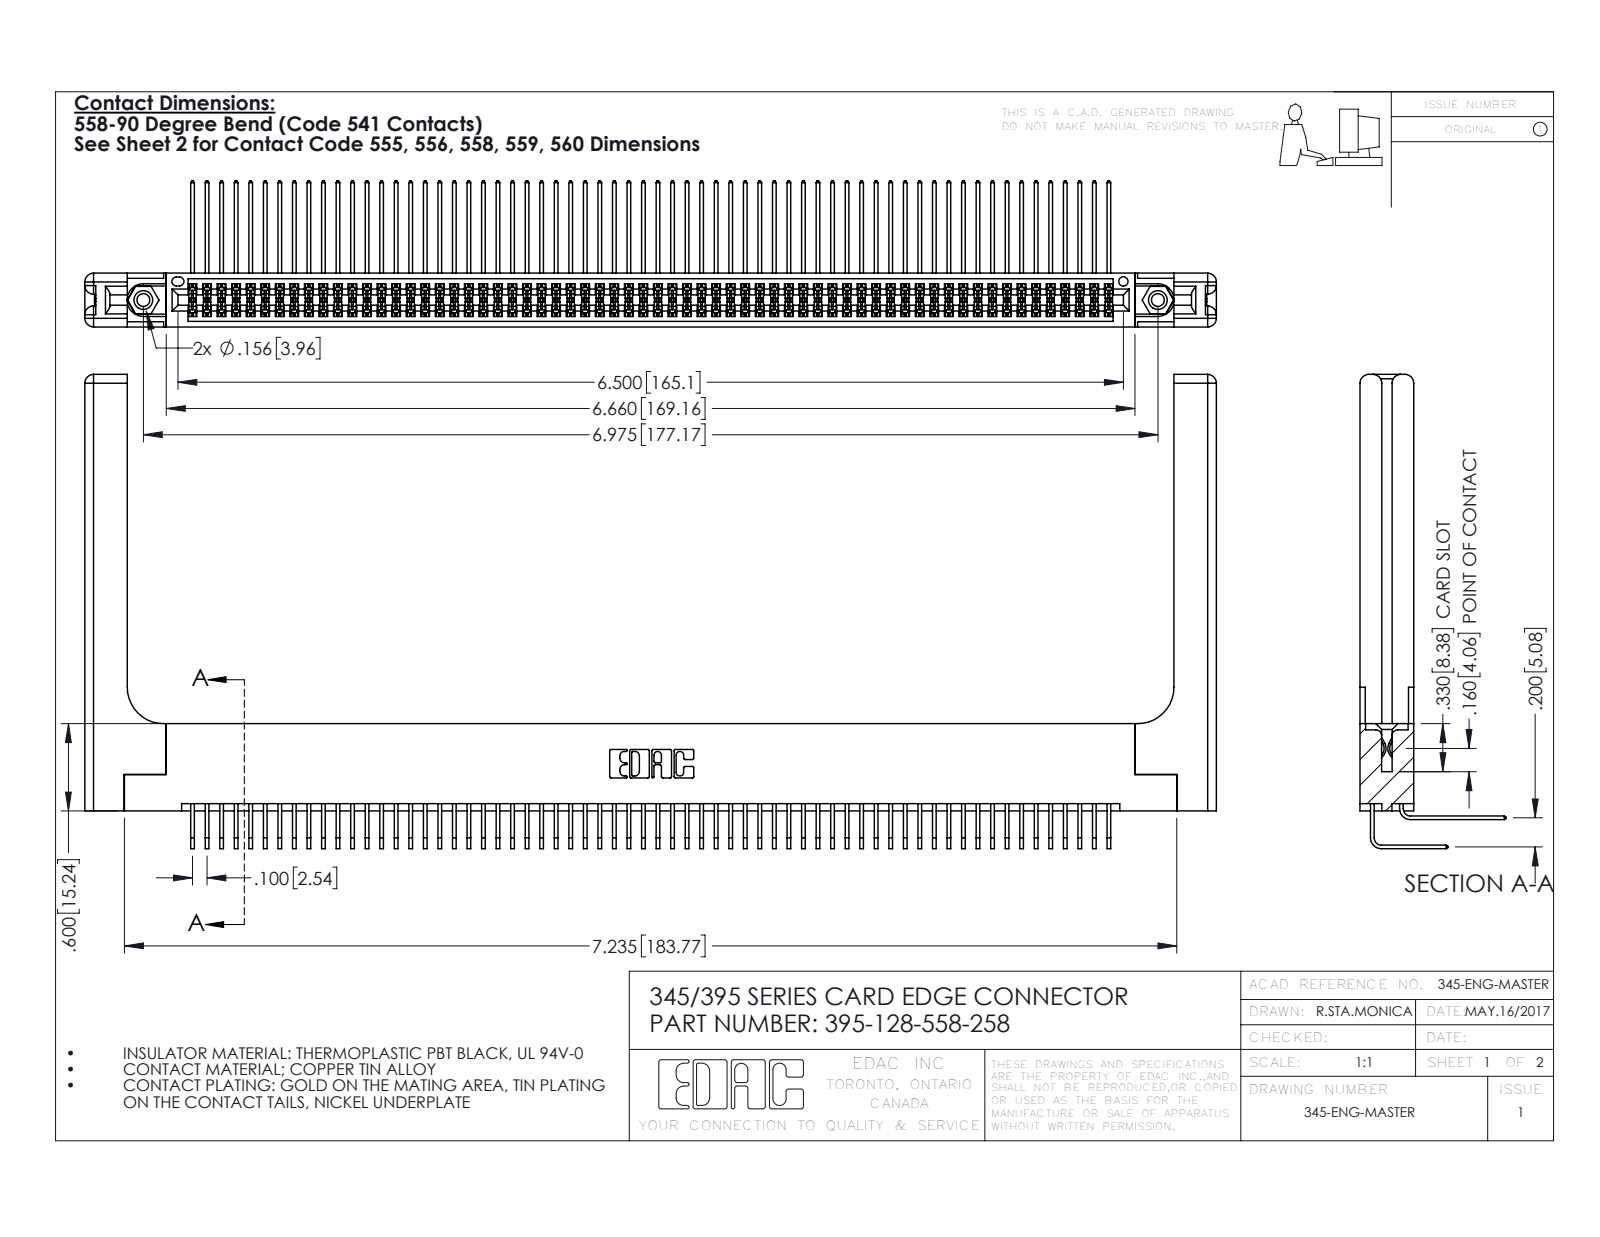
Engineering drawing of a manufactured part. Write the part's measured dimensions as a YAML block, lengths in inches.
part_name: "345-250-001_345-250-001-102; 345-292-001_558 559 Tail - 1; 345-220-058_345-220-058; 345 Part_Flush Mounting Lugs - 0.156 Dia-TH (+2 more)"
step_written_by: "SolidWorks 2016 (CONFIG_CONTROL_DESIGN)"
units: inches
bodies: {solids: 133, faces: 7038, planar: 4708, cylindrical: 2270, other: 60}
overall_size: [7.779, 3.259, 1.005]
volume: 1.746
surface_area: 60.02
round_holes:
  - {diameter: 0.089, count: 2}
  - {diameter: 0.125, count: 2}
  - {diameter: 0.156, count: 2}
  - {diameter: 0.064, count: 1}
round_bosses_or_shafts:
  - {diameter: 0.155, count: 2}
partial_cylinders:
  - {radius: 0.006, count: 193}
  - {radius: 0.01, count: 22}
  - {radius: 0.06, count: 16}
  - {radius: 0.007, count: 6}
  - {radius: 0.031, count: 6}
  - {radius: 0.026, count: 3}
  - {radius: 0.014, count: 2}
  - {radius: 0.019, count: 2}
face_to_face_distances: [0.072, 0.298, 0.2, 0.37, 0.098, 0.272, 0.025, 0.225, 0.025, 0.148]
hole_center_spacings: [0.27, 6.739, 6.975]
